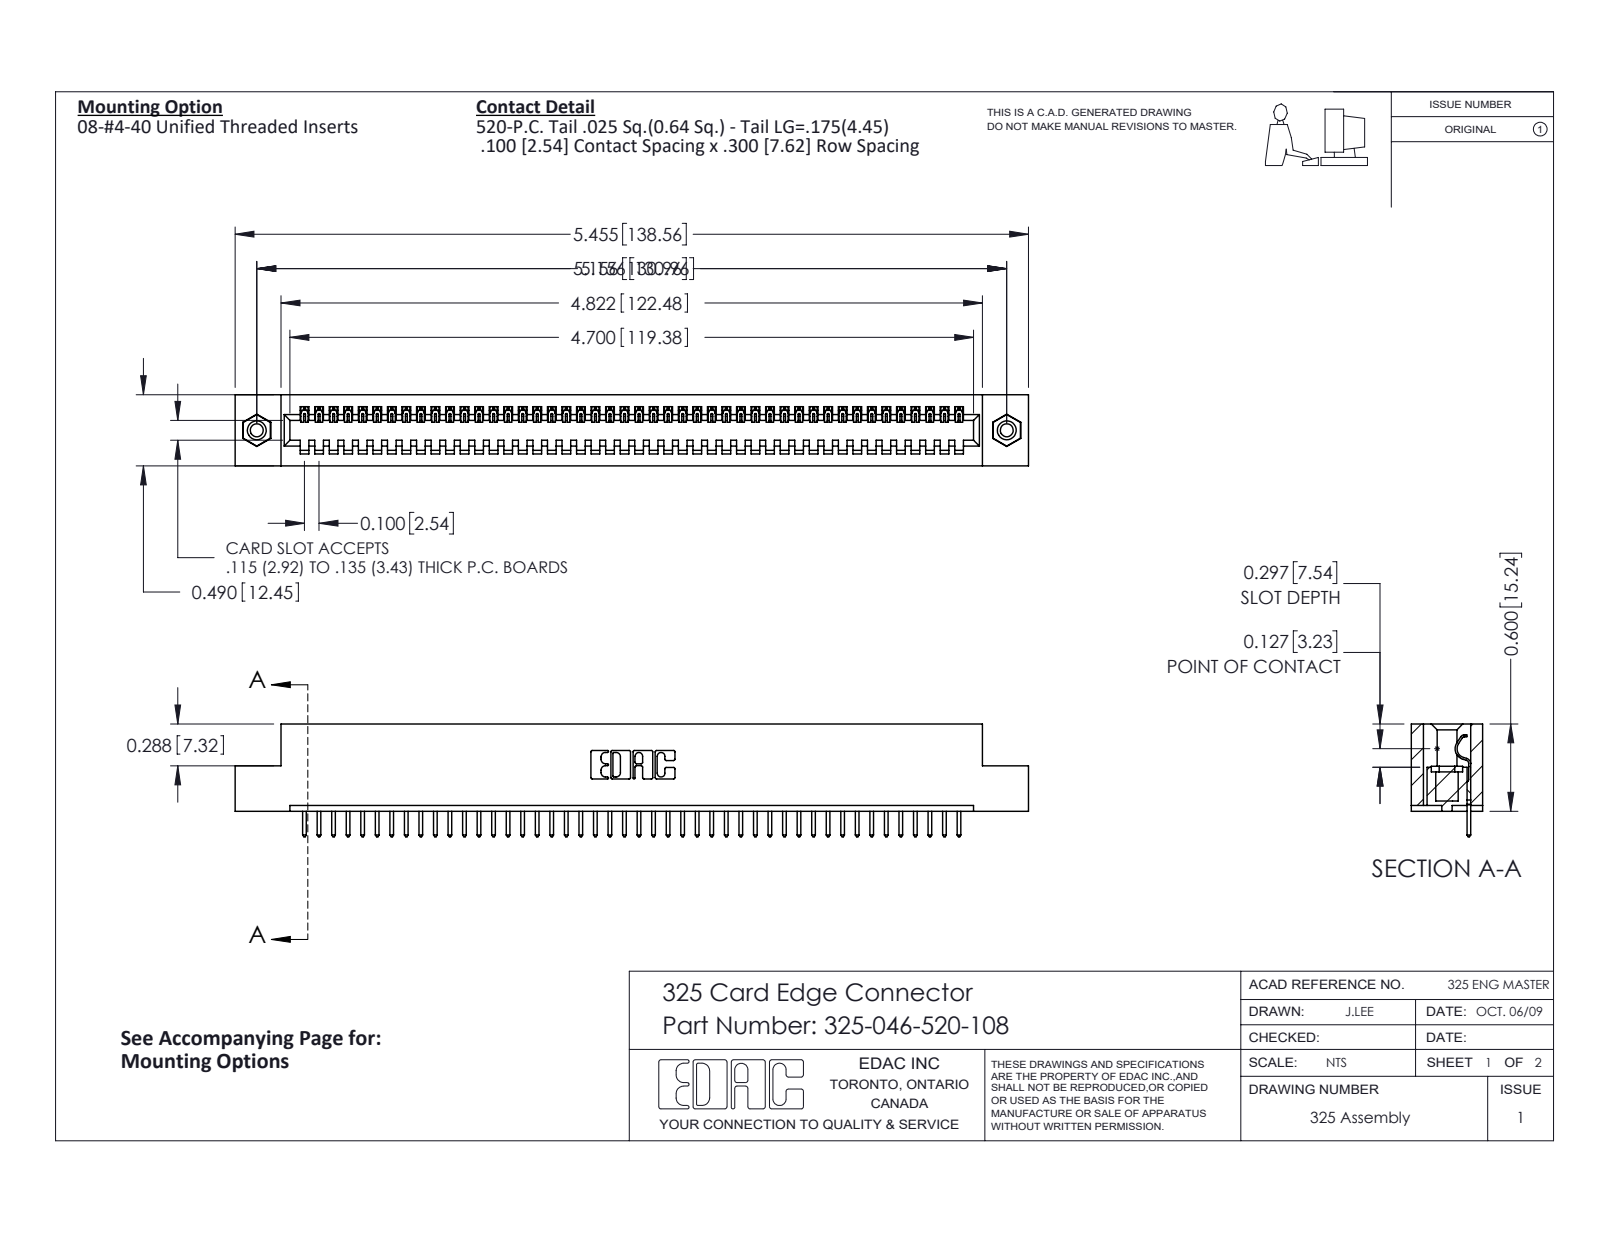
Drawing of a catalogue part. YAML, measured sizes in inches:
part_name: "345-250-001_345-250-003-102; 325-292-001_325-293-120; 325 Part_TI; 325-046-520-108"
step_written_by: "SolidWorks 2016 (CONFIG_CONTROL_DESIGN)"
units: inches
bodies: {solids: 49, faces: 2842, planar: 2034, cylindrical: 792, other: 16}
overall_size: [5.455, 0.775, 0.49]
volume: 1.068
surface_area: 29.01
round_holes:
  - {diameter: 0.089, count: 2}
  - {diameter: 0.125, count: 2}
  - {diameter: 0.16, count: 2}
round_bosses_or_shafts:
  - {diameter: 0.155, count: 2}
partial_cylinders:
  - {radius: 0.006, count: 92}
  - {radius: 0.01, count: 92}
  - {radius: 0.01, count: 22}
  - {radius: 0.007, count: 6}
  - {radius: 0.031, count: 6}
  - {radius: 0.026, count: 3}
  - {radius: 0.014, count: 1}
  - {radius: 0.022, count: 1}
face_to_face_distances: [0.083, 0.407, 0.49, 0.3, 0.107, 0.383, 0.025, 0.325, 0.56, 0.263]
hole_center_spacings: [5.156]
